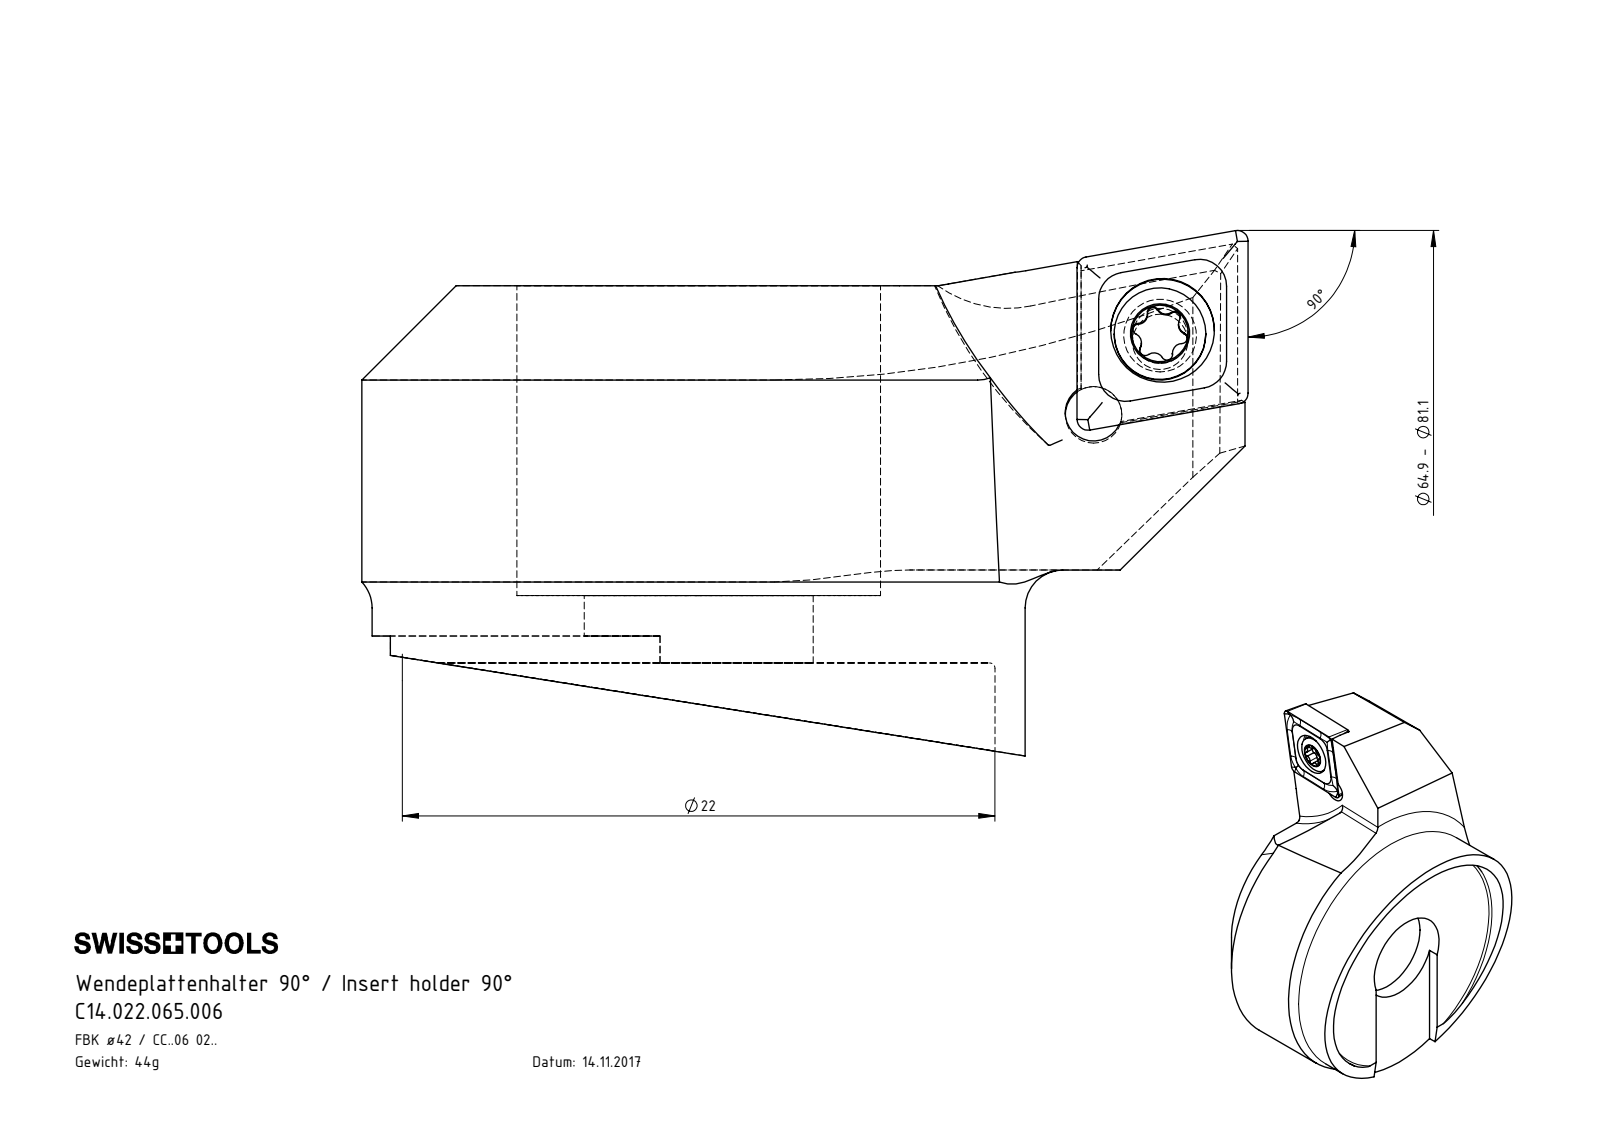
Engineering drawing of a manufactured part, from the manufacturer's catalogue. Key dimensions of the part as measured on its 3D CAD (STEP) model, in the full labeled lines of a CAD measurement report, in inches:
Part name (STEP PRODUCT): F42-WCA.001.016_A_fertigbearbeitet; CCMT060204; WCA-ER2.001.006_A; C14.022.065.006
STEP written by: SolidWorks 2017 (CONFIG_CONTROL_DESIGN)
Units: inches
Bodies: 5 solids, 151 faces (48 planar, 47 cylindrical, 56 other)
Overall size (bounding box): 1.295 × 0.984 × 0.768
Volume: 0.343 in³ · Surface area: 5.504 in²
Round holes (diameter × count): ⌀0.081 ×1, ⌀0.083 ×1, ⌀0.11 ×1, ⌀0.152 ×1, ⌀0.335 ×1, ⌀0.531 ×1
Round bosses / shafts (diameter × count): ⌀0.955 ×1, ⌀0.134 ×1, ⌀0.098 ×1
Partial cylindrical surfaces — rounded edges, fillets, slot ends (radius × count): R0.008 ×6, R0.014 ×5, R0.02 ×2, R0.014 ×1, R0.197 ×1, R0.433 ×1, R0.492 ×1, R0.63 ×1
Main face-to-face distances: 0.551, 0.539, 0.453, 0.441, 0.098, 0.09, 0.512, 0.5, 0.059, 0.039
Hole centre spacings: 0.151, 0.157
